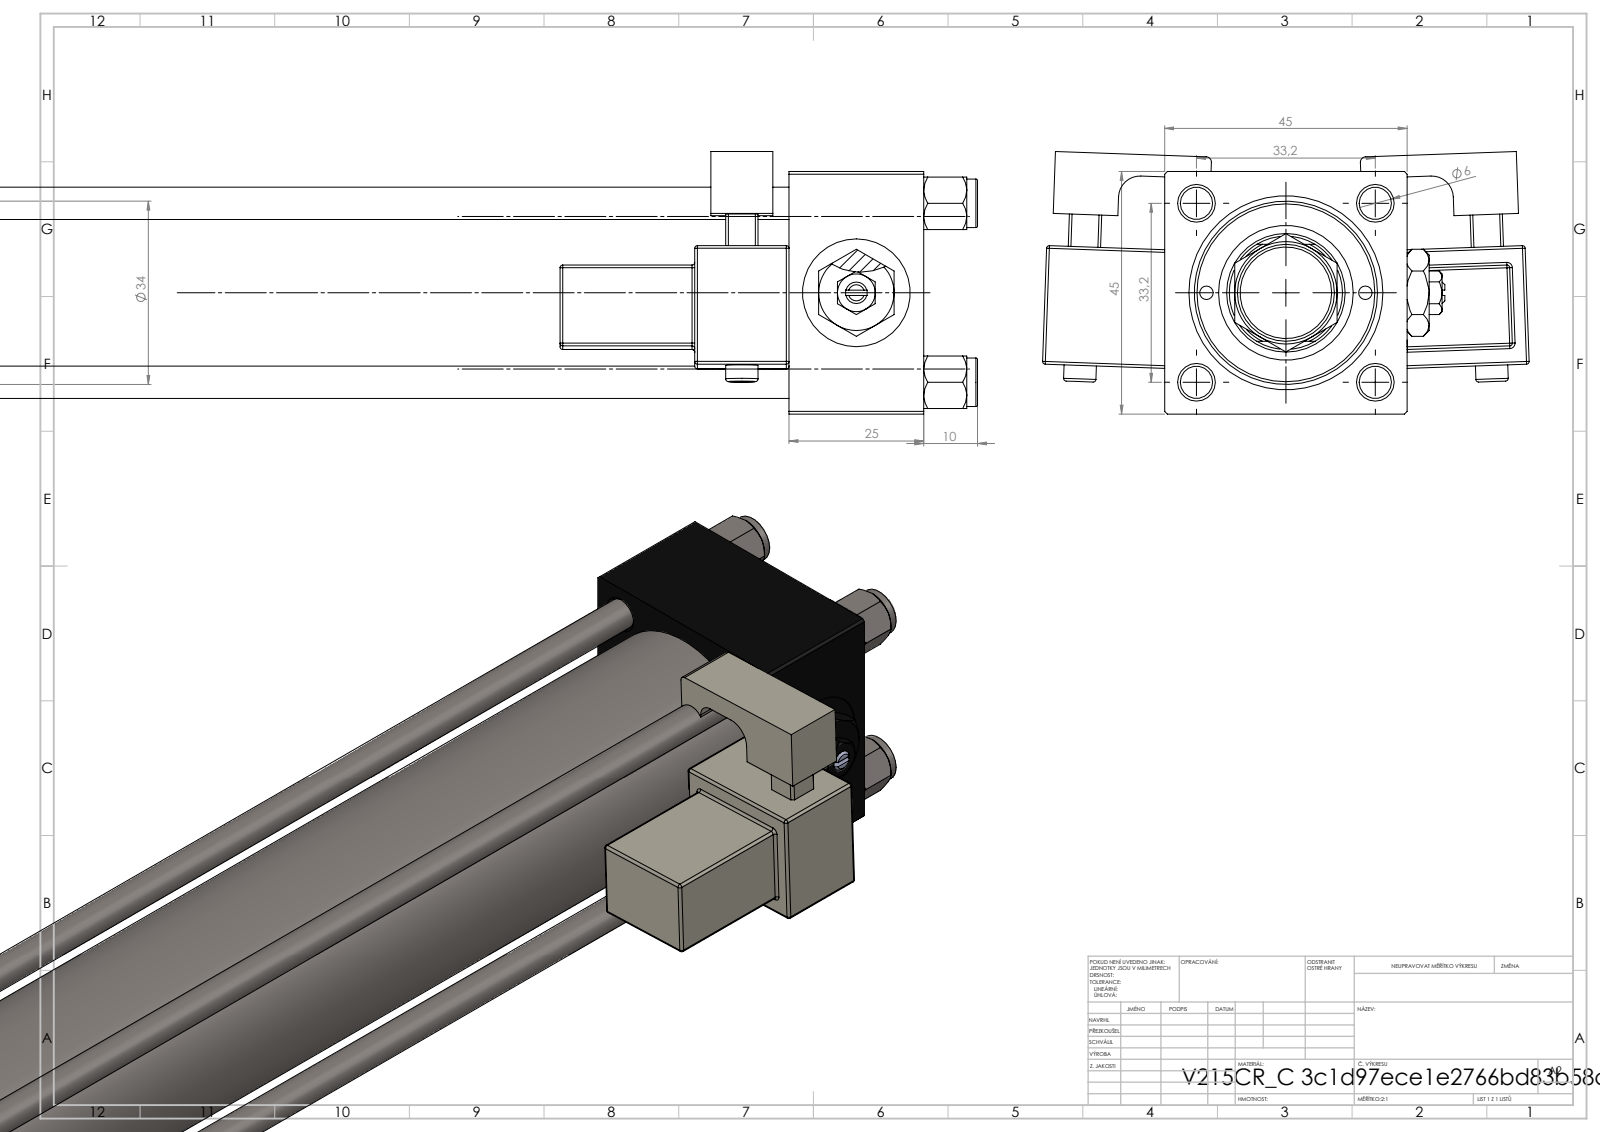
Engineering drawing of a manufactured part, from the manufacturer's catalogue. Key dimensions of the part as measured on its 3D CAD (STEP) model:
Part name (STEP PRODUCT): NUT_M5_C; V215CR_C_TYCINKA; V215_VC_A; V215CR_VCP_C (+4 more)
STEP written by: SolidWorks 2019 (CONFIG_CONTROL_DESIGN)
Units: millimetres
Bodies: 16 solids, 1464 faces (652 planar, 166 cylindrical, 646 other)
Overall size (bounding box): 471 × 90.31 × 48.72
Volume: 487 332 mm³ · Surface area: 190 147 mm²
Round holes (diameter × count): ⌀6 ×4, ⌀2.5 ×2, ⌀7 ×2, ⌀13.16 ×2, ⌀20 ×2, ⌀10.5 ×1, ⌀22 ×1, ⌀24 ×1, ⌀25 ×1, ⌀32 ×1, ⌀33 ×1
Round bosses / shafts (diameter × count): ⌀9 ×4, ⌀6 ×2, ⌀38 ×1, ⌀34 ×1, ⌀18 ×1, ⌀11 ×1
Partial cylindrical surfaces — rounded edges, fillets, slot ends (radius × count): R0.5 ×48, R1 ×2, R2.5 ×2, R4 ×2, R10.5 ×1
Main face-to-face distances: 45, 25, 3, 355, 330, 403, 22.99, 312.5, 378, 44.8
Hole centre spacings: 16.7, 23.48, 33.2, 35.47, 14.75, 46.95, 29.5, 355.5
